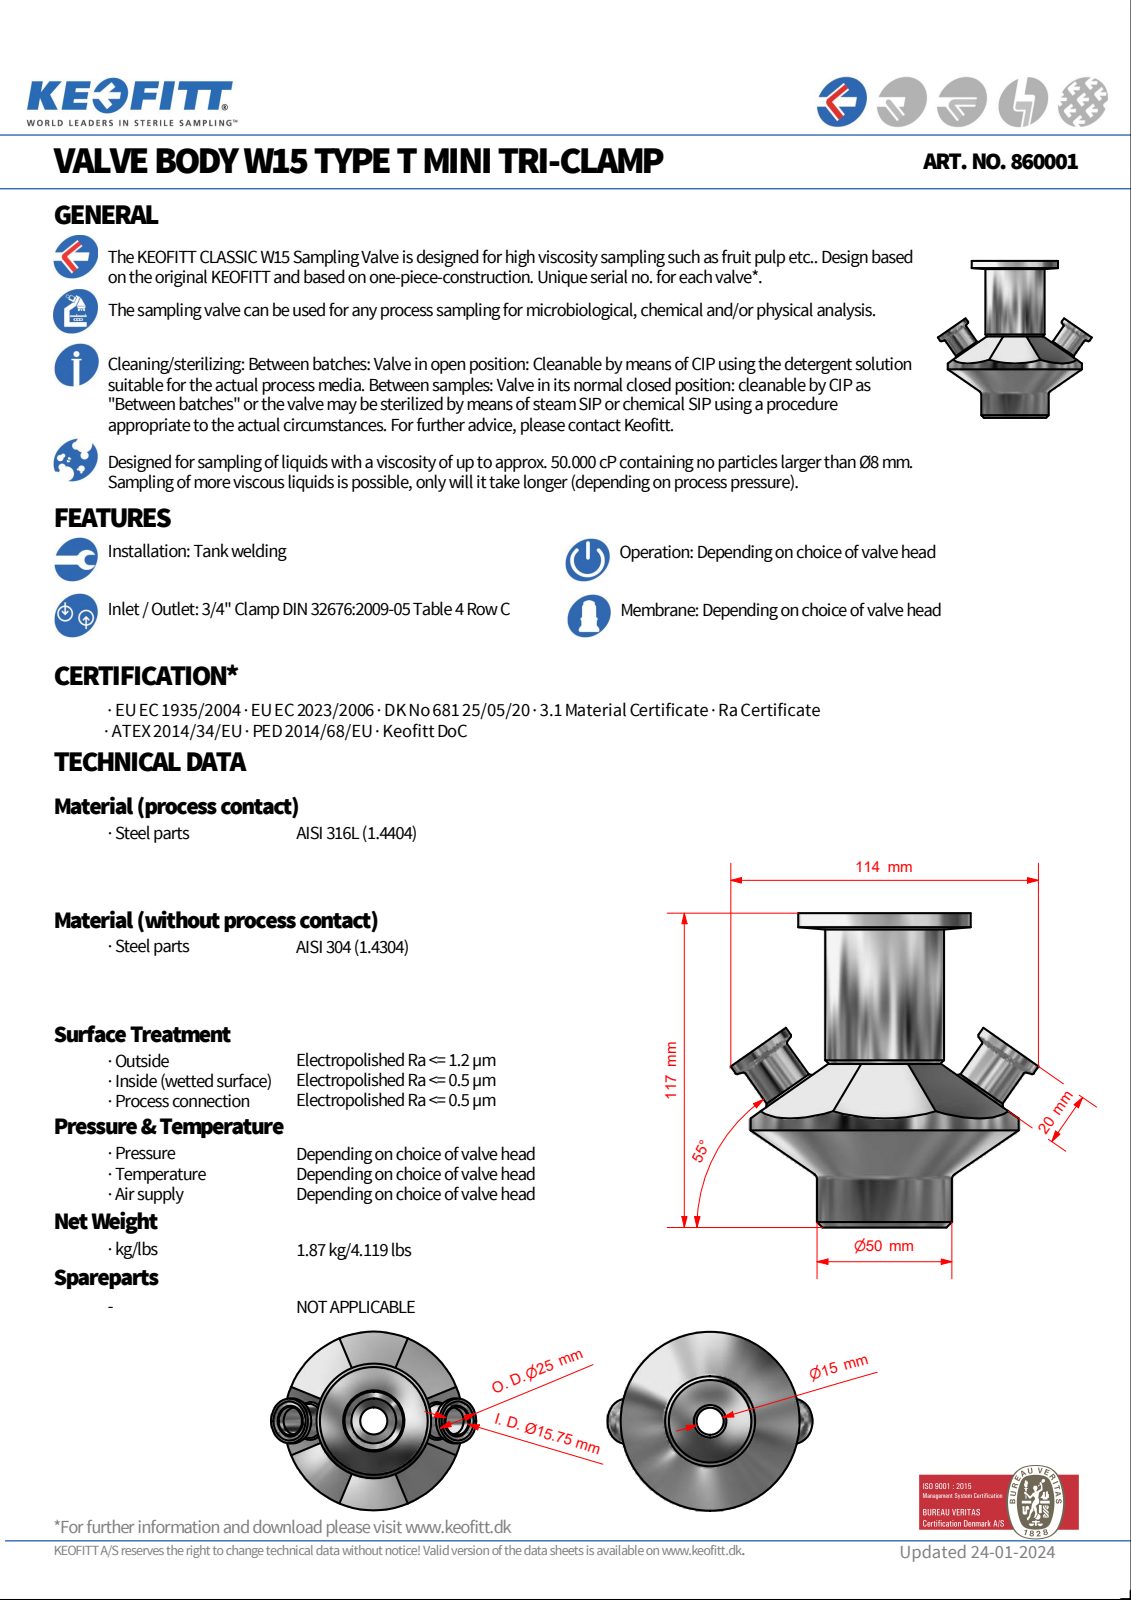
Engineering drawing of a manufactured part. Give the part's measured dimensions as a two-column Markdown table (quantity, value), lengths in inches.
| quantity | value |
| --- | --- |
| part name | 860001 step |
| STEP written by | Autodesk Inventor 2017 (AUTOMOTIVE_DESIGN) |
| units | inches |
| bodies | 1 solid, 71 faces (20 planar, 20 cylindrical, 31 other) |
| overall size | 4.594 × 4.483 × 3.917 |
| volume | 19.57 in³ |
| surface area | 68.57 in² |
| round holes (diameter × count) | 0.591 × 2, 0.62 × 2, 1.535 × 1, 2.362 × 1 |
| round bosses / shafts (diameter × count) | 0.984 × 2, 0.748 × 2, 3.917 × 1, 2.52 × 1, 1.969 × 1, 1.732 × 1, 1.496 × 1, 1.453 × 1 |
| main face-to-face distances | 4.516, 4.525, 4.594, 0.079, 0.07, 2.386, 2.13, 2.139, 2.209, 0.787 |
